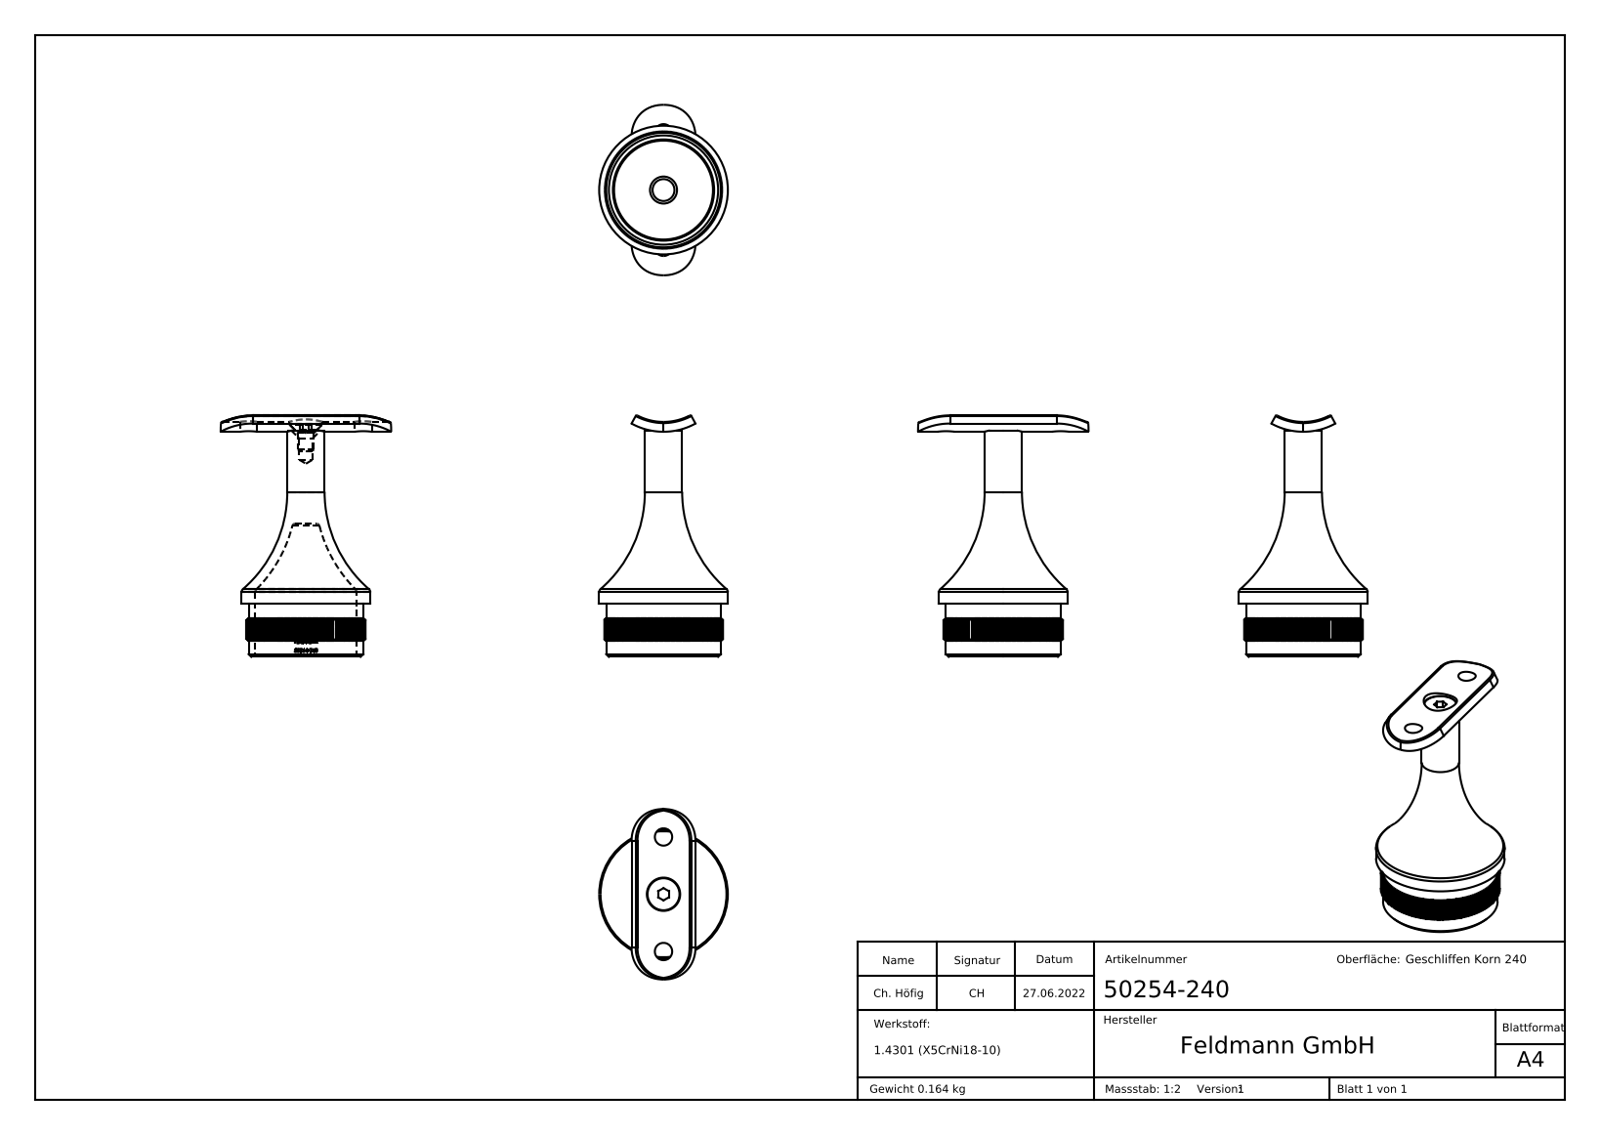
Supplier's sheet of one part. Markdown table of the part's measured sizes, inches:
| quantity | value |
| --- | --- |
| part name | 5025x-240 Teil2_5025x-240 Teil2; DIN 7991 Konfig_DIN 7991 M6x10; 5025x-240 Teil1_50254-240 Teil1; 50254-240 |
| STEP written by | SolidWorks 2018 (CONFIG_CONTROL_DESIGN) |
| units | inches |
| bodies | 3 solids, 1075 faces (445 planar, 200 cylindrical, 430 other) |
| overall size | 3.569 × 2.52 × 1.902 |
| volume | 1.751 in³ |
| surface area | 28.86 in² |
| round holes (diameter × count) | 0.256 × 2, 0.197 × 1, 0.319 × 1, 0.492 × 1, 1.496 × 1 |
| round bosses / shafts (diameter × count) | 1.902 × 1, 1.693 × 1, 0.551 × 1, 0.472 × 1, 0.236 × 1 |
| partial cylindrical surfaces (radius × count) | 0.472 × 4, 0.02 × 2, 0.28 × 1, 0.752 × 1, 0.835 × 1, 0.877 × 1, 0.98 × 1 |
| main face-to-face distances | 0.846, 0.847, 0.847, 0.846, 0.846, 0.787, 3.346, 2.559, 3.439, 2.652 |
| hole center spacings | 0.846, 1.693 |
